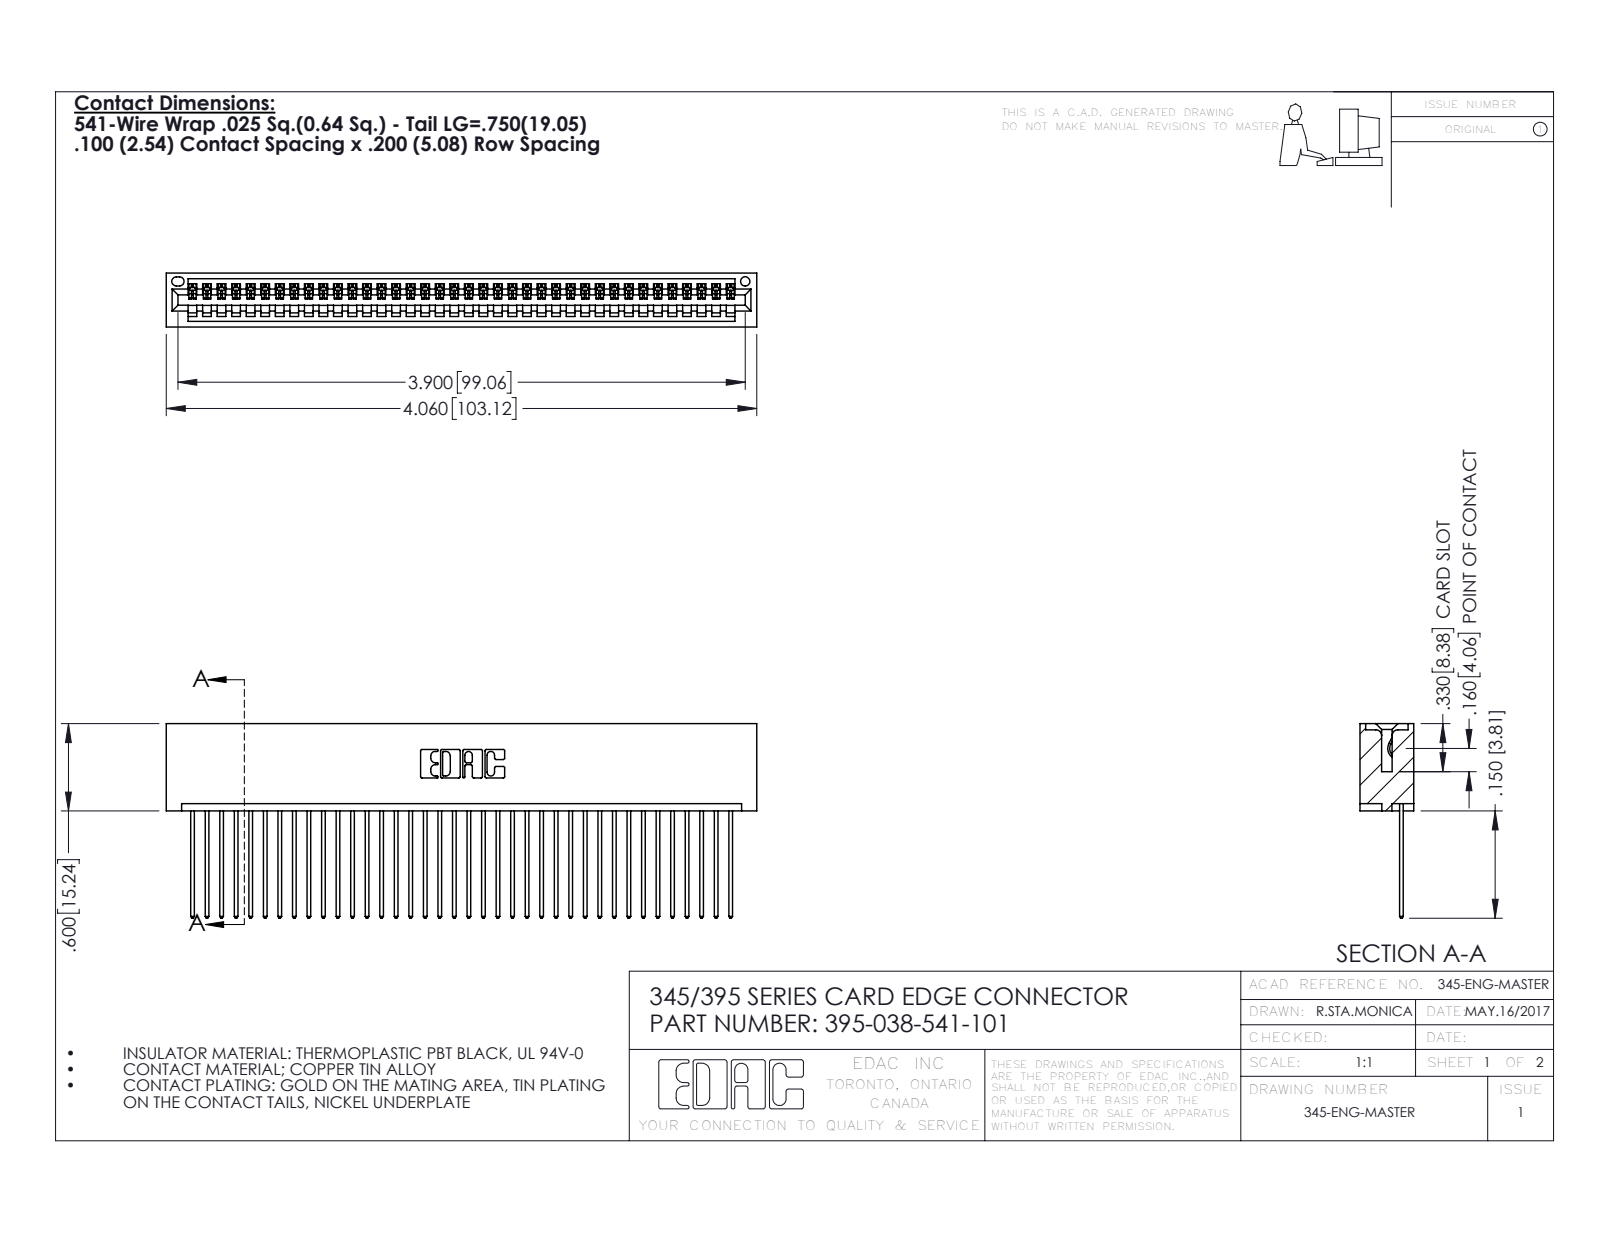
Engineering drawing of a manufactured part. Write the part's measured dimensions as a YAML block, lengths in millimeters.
part_name: "345 Part_No Mounting Lugs; 345-292-001_345-293-141; 395-038-541-101"
step_written_by: "SolidWorks 2016 (CONFIG_CONTROL_DESIGN)"
units: millimeters
bodies: {solids: 39, faces: 2322, planar: 1596, cylindrical: 726, other: 0}
overall_size: [103.1, 34, 9.4]
volume: 10500
surface_area: 14790
round_holes:
  - {diameter: 1.6, count: 1}
partial_cylinders:
  - {radius: 0.2, count: 76}
  - {radius: 0.3, count: 76}
  - {radius: 0.3, count: 22}
  - {radius: 0.2, count: 6}
  - {radius: 0.8, count: 6}
  - {radius: 0.7, count: 3}
  - {radius: 0.8, count: 2}
  - {radius: 1, count: 2}
face_to_face_distances: [1.8, 7.6, 2.5, 6.9, 0.6, 5.1, 9.4, 5.7, 3.8, 1.8]
